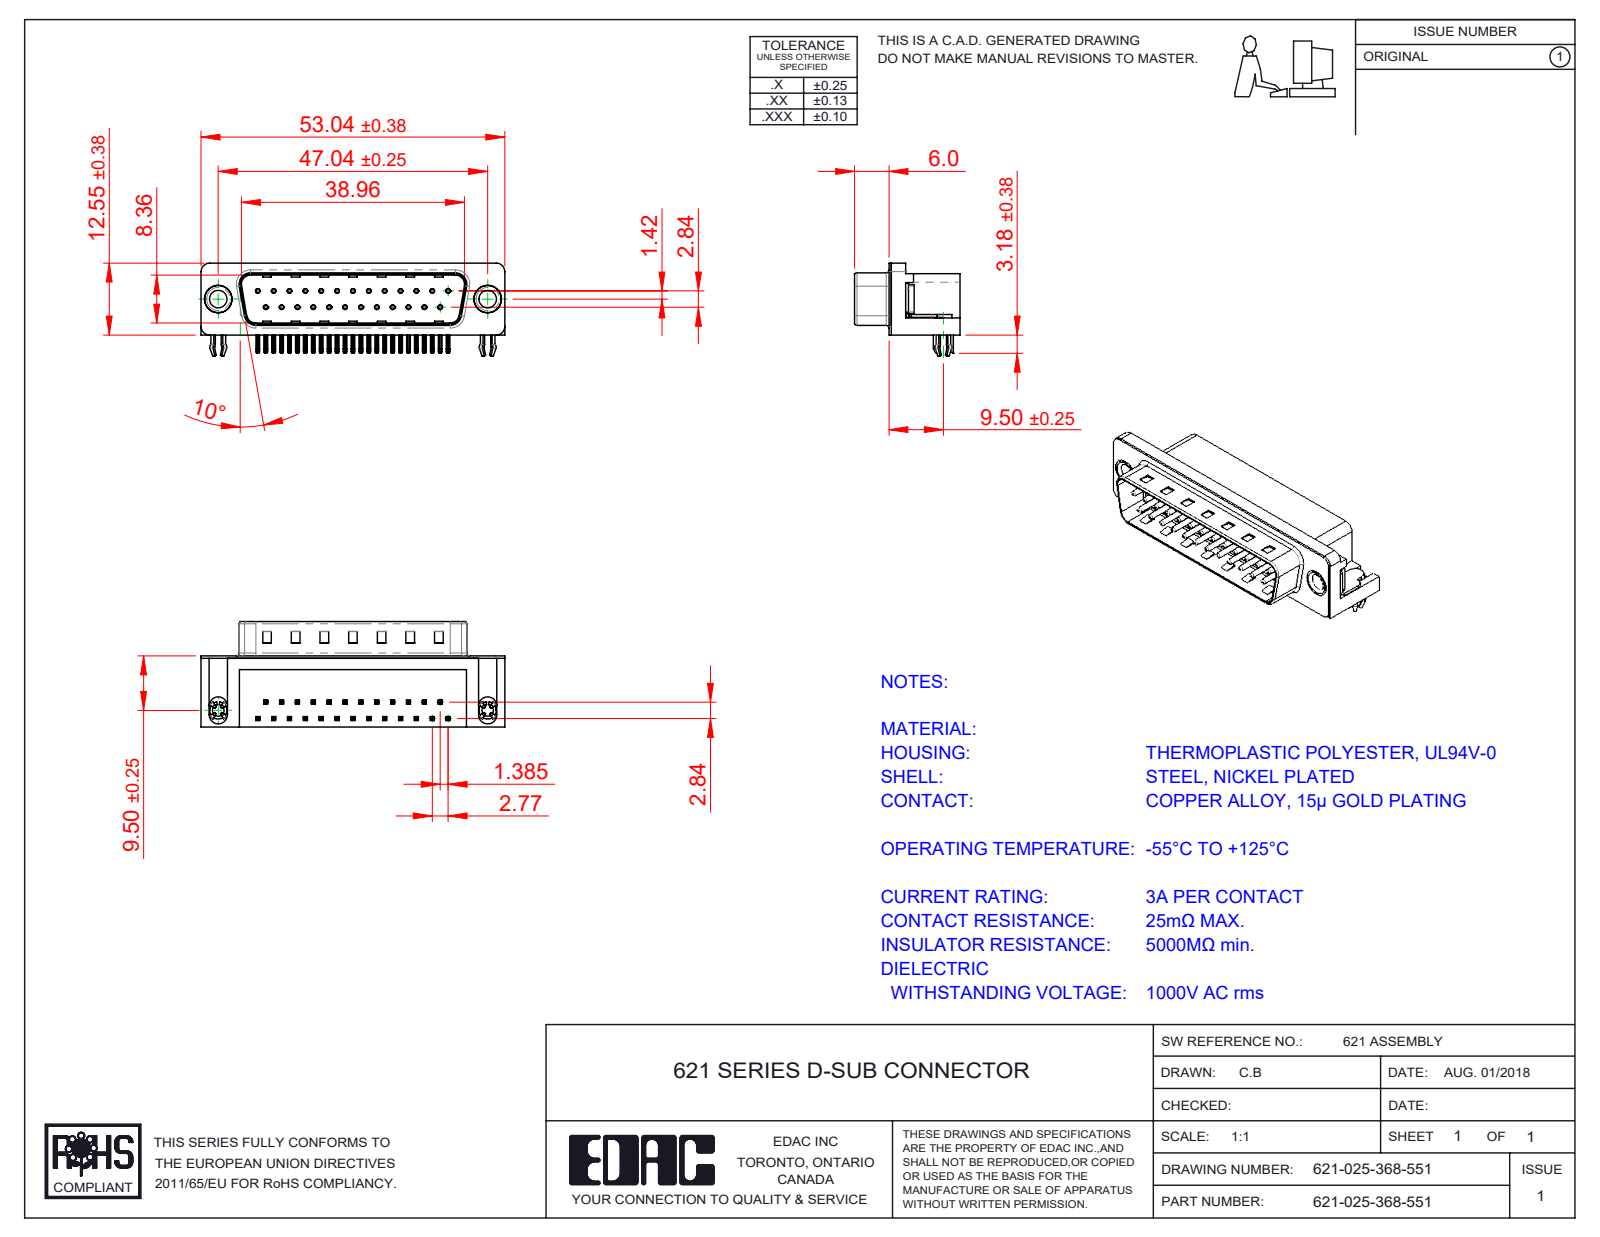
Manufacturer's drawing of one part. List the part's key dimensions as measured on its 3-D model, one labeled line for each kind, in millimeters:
Part name (STEP PRODUCT): 621 Contact Top; 621 Housing_25 Socket; 621 Thru Hole Rivet; 621 4-40 Threaded Board Mount (+3 more)
STEP written by: SolidWorks 2016 (CONFIG_CONTROL_DESIGN)
Units: millimetres
Bodies: 31 solids, 2253 faces (1405 planar, 653 cylindrical, 195 other)
Overall size (bounding box): 53.04 × 18.4 × 15.73
Volume: 6 347 mm³ · Surface area: 7 738 mm²
Round holes (diameter × count): ⌀0.35 ×25, ⌀0.8 ×25, ⌀2.26 ×2, ⌀3.05 ×2, ⌀4 ×2, ⌀4.8 ×2, ⌀5 ×2
Round bosses / shafts (diameter × count): ⌀0.75 ×25, ⌀4.9 ×2, ⌀4.75 ×2, ⌀3.85 ×2, ⌀3.26 ×2
Partial cylindrical surfaces — rounded edges, fillets, slot ends (radius × count): R0.25 ×108, R0.12 ×50, R1 ×16, R0.5 ×9, R1.6 ×8, R1.5 ×7, R0.9 ×4, R2 ×4
Main face-to-face distances: 0.4, 12, 10.35, 2.1, 8.76, 10.46, 1.7, 10.86, 12.4, 9
Hole centre spacings: 3.16, 2.77, 5.54, 8.31, 11.08, 13.85, 16.62, 5.03
